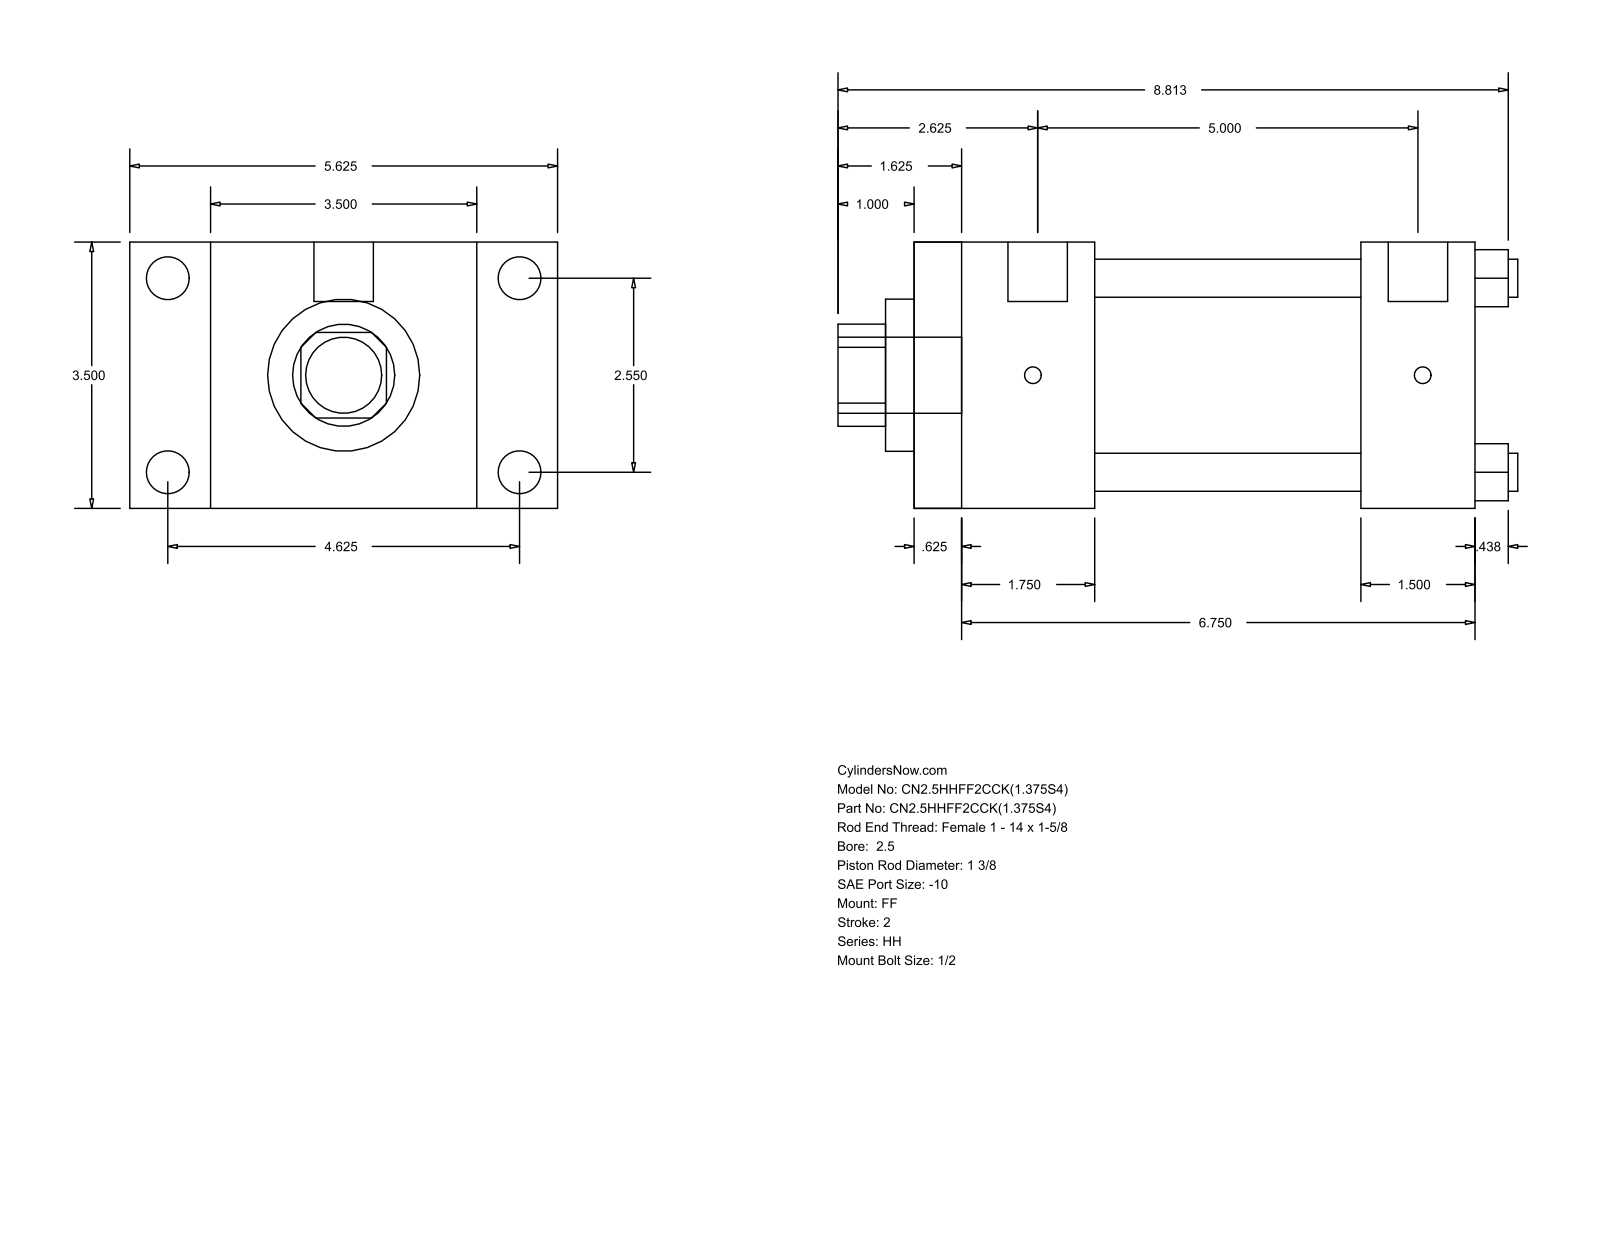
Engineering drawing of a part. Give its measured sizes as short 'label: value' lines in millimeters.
name: HH_FF__0250_1.375
written by: GSSL Pune (CONFIG_CONTROL_DESIGN)
unit: mm
bodies: 0 solids, 92 faces (64 planar, 28 cylindrical, 0 other)
size: 227.01 × 142.88 × 88.9
holes: 4× ⌀12.7, 1× ⌀34.92, 1× ⌀50.8, 1× ⌀73.03
bosses: 4× ⌀14.3, 4× ⌀5.56, 2× ⌀19.84, 1× ⌀25.4
rounds: 1× R17.06
face distances: 88.9, 187.32, 15.87, 171.45, 60.32, 44.45, 127, 149.22, 133.35, 38.1
hole spacings: 45.79, 64.76, 91.58
